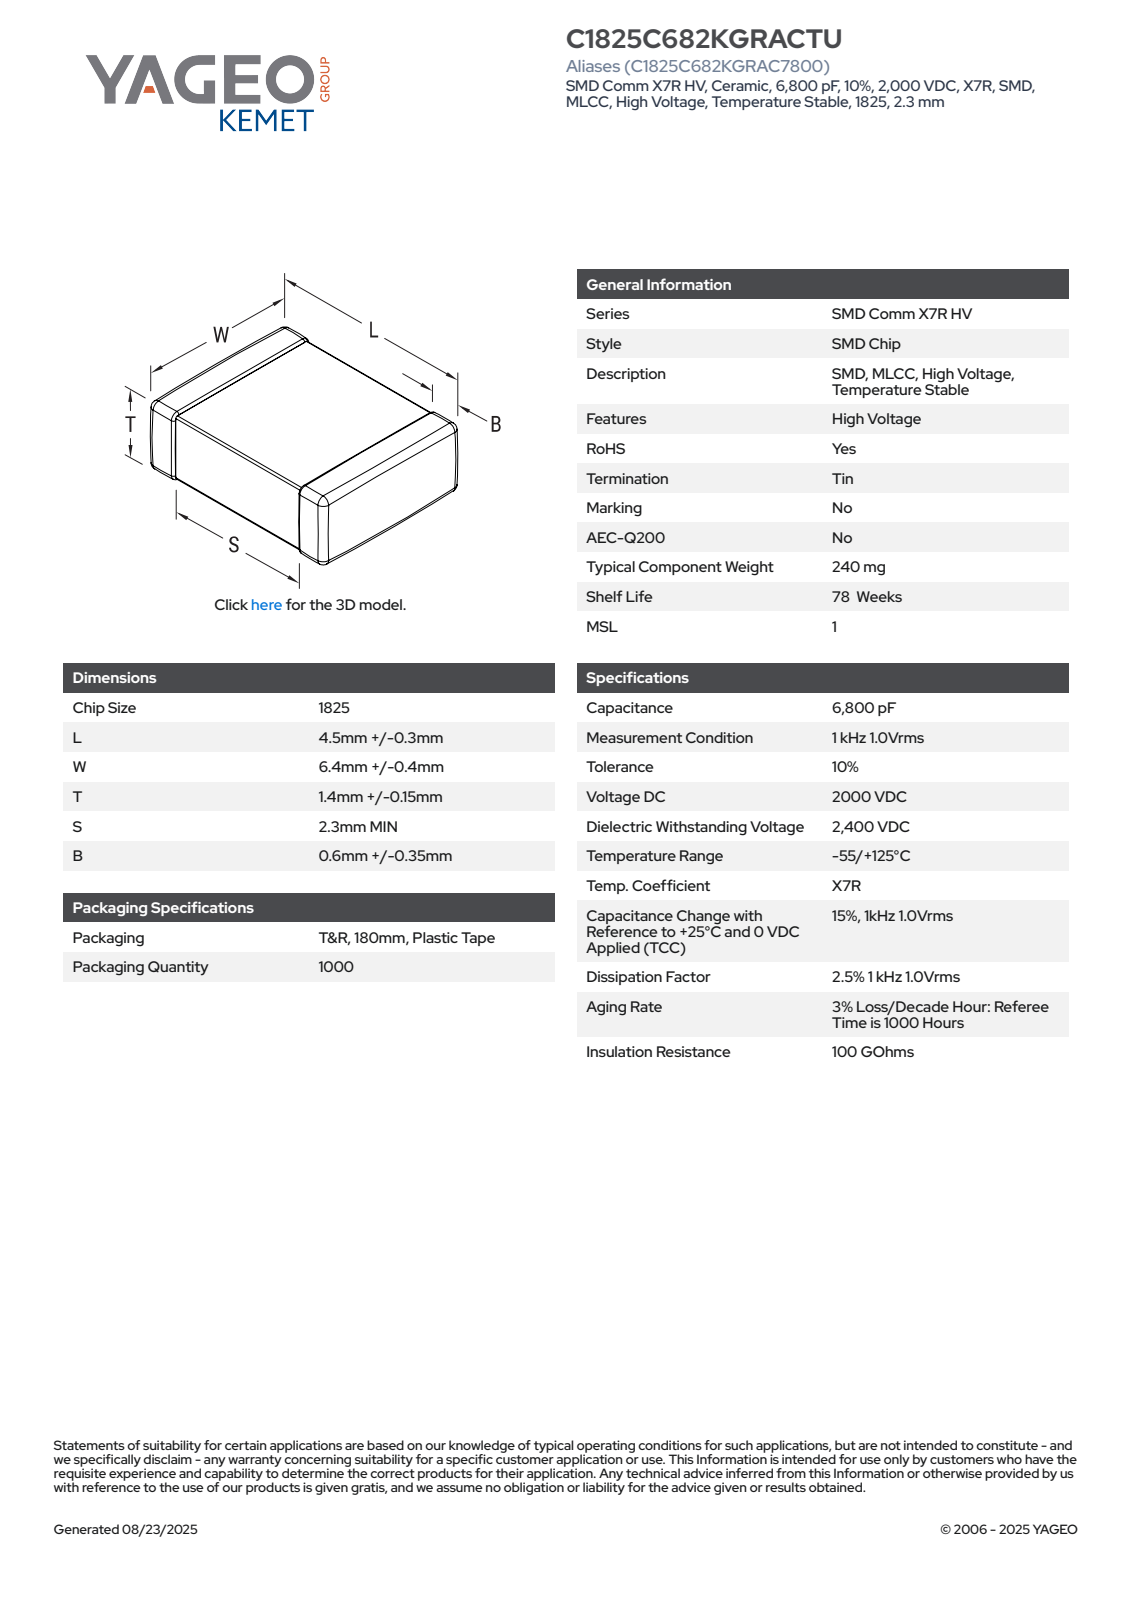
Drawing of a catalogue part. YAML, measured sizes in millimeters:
part_name: "CCS_CCSTDNOS_1825_L4.8W6.8T1.55B0.95"
step_written_by: "SolidWorks 2014 (AUTOMOTIVE_DESIGN)"
units: millimeters
bodies: {solids: 4, faces: 125, planar: 71, cylindrical: 38, other: 16}
overall_size: [6.8, 4.8, 1.55]
volume: 44
surface_area: 98
partial_cylinders:
  - {radius: 0.14, count: 24}
face_to_face_distances: [1.27, 1.41, 1.55, 4.8, 6.66, 6.52, 6.8, 0.34, 3.56, 3.42]
